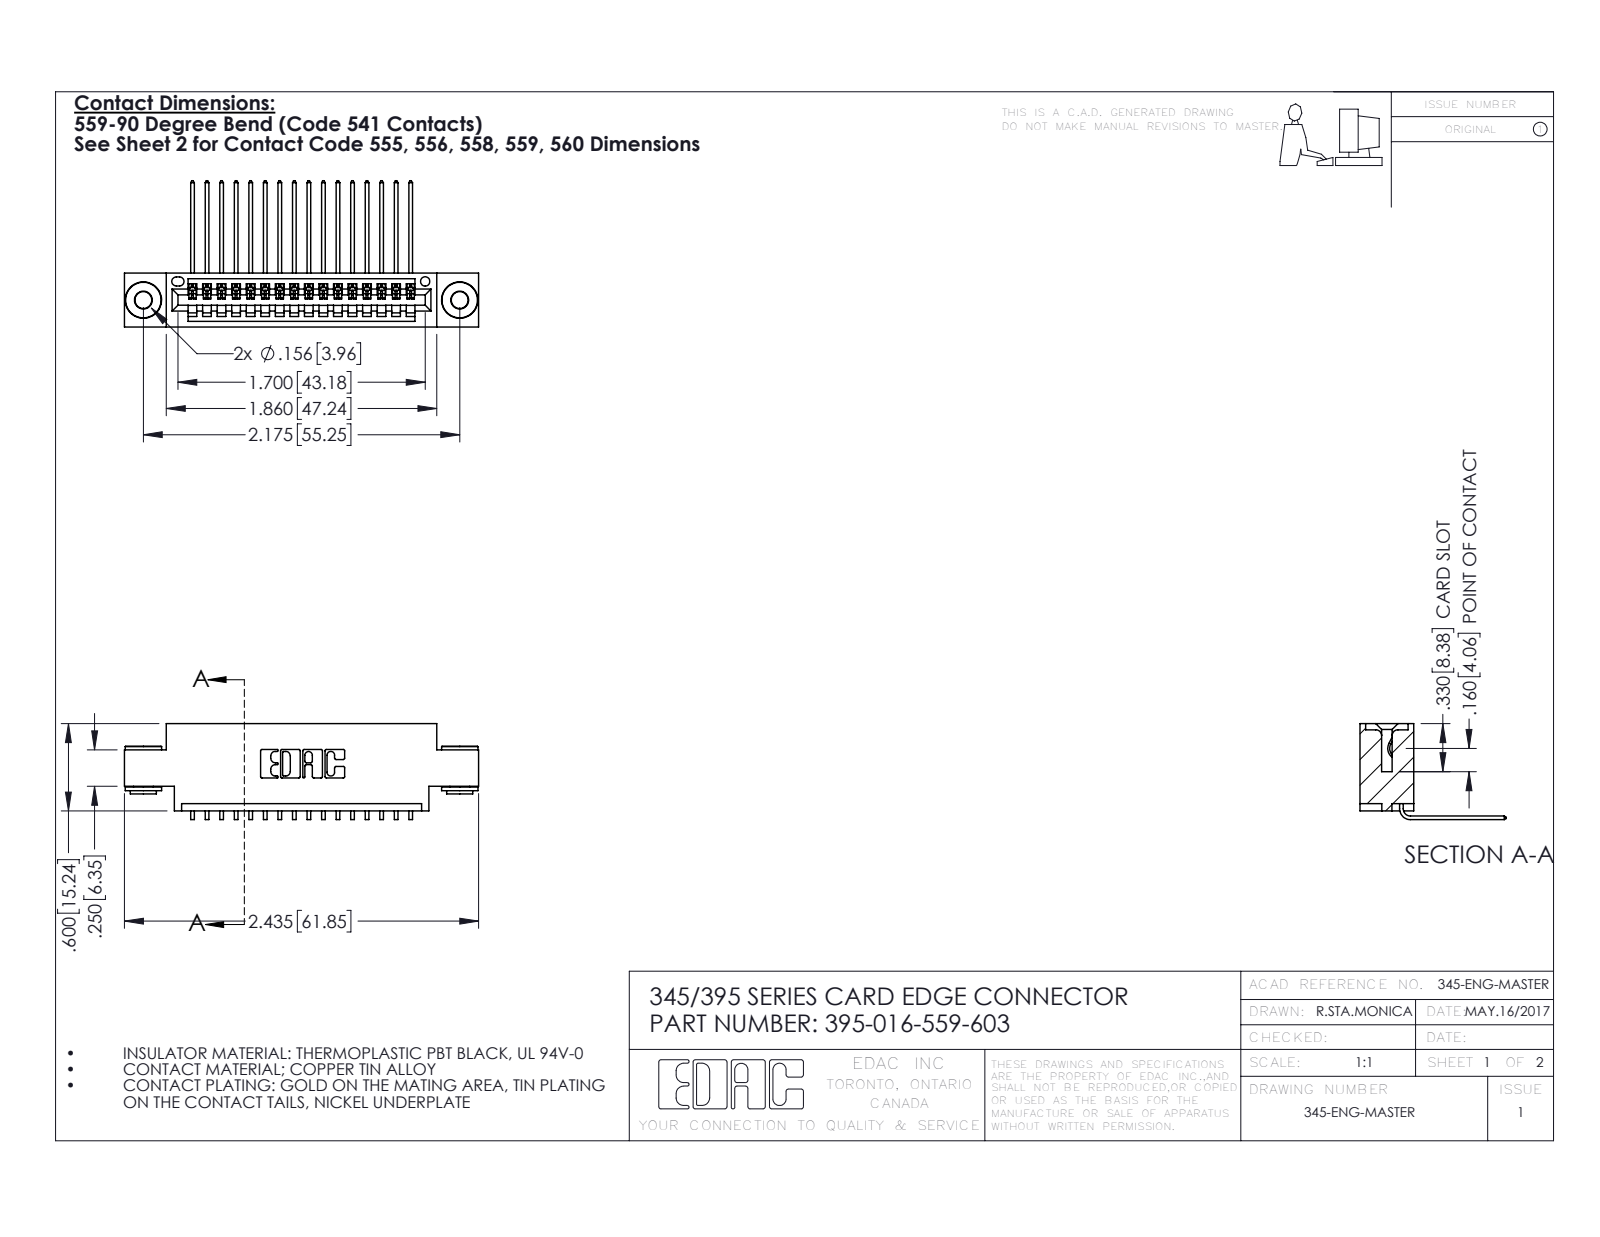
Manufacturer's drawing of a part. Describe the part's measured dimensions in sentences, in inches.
The part is named "345 Part_0.170 Offset - 0.156 Dia-TH; 395-016-559-603; 345-292-001_558 559 Tail - 1; 345-250-002_345-250-002-102". Its 3-D file was written by "SolidWorks 2016 (CONFIG_CONTROL_DESIGN)". It is 19 solids with 1128 faces: 766 planar, 354 cylindrical and 8 other. Overall it measures 2.435 by 1.005 by 0.659 inches. Its volume is 0.343 cubic inches and its surface area 12.04 square inches. Round holes: 2 of diameter 0.116, 2 of diameter 0.156, 1 of diameter 0.064. Round bosses or shafts: 2 of diameter 0.25, 2 of diameter 0.18, 2 of diameter 0.136. Partial cylindrical surfaces (rounded edges, fillets, slot ends): 32 of radius 0.006, 22 of radius 0.01, 6 of radius 0.007, 6 of radius 0.031, 3 of radius 0.026, 2 of radius 0.031, 2 of radius 0.04, 1 of radius 0.014. The main face-to-face distances are 0.37, 0.072, 0.298, 0.2, 0.098, 0.272, 0.025, 0.1, 0.175, 0.225. The hole center spacings are 0.27, 1.942, 2.175.
